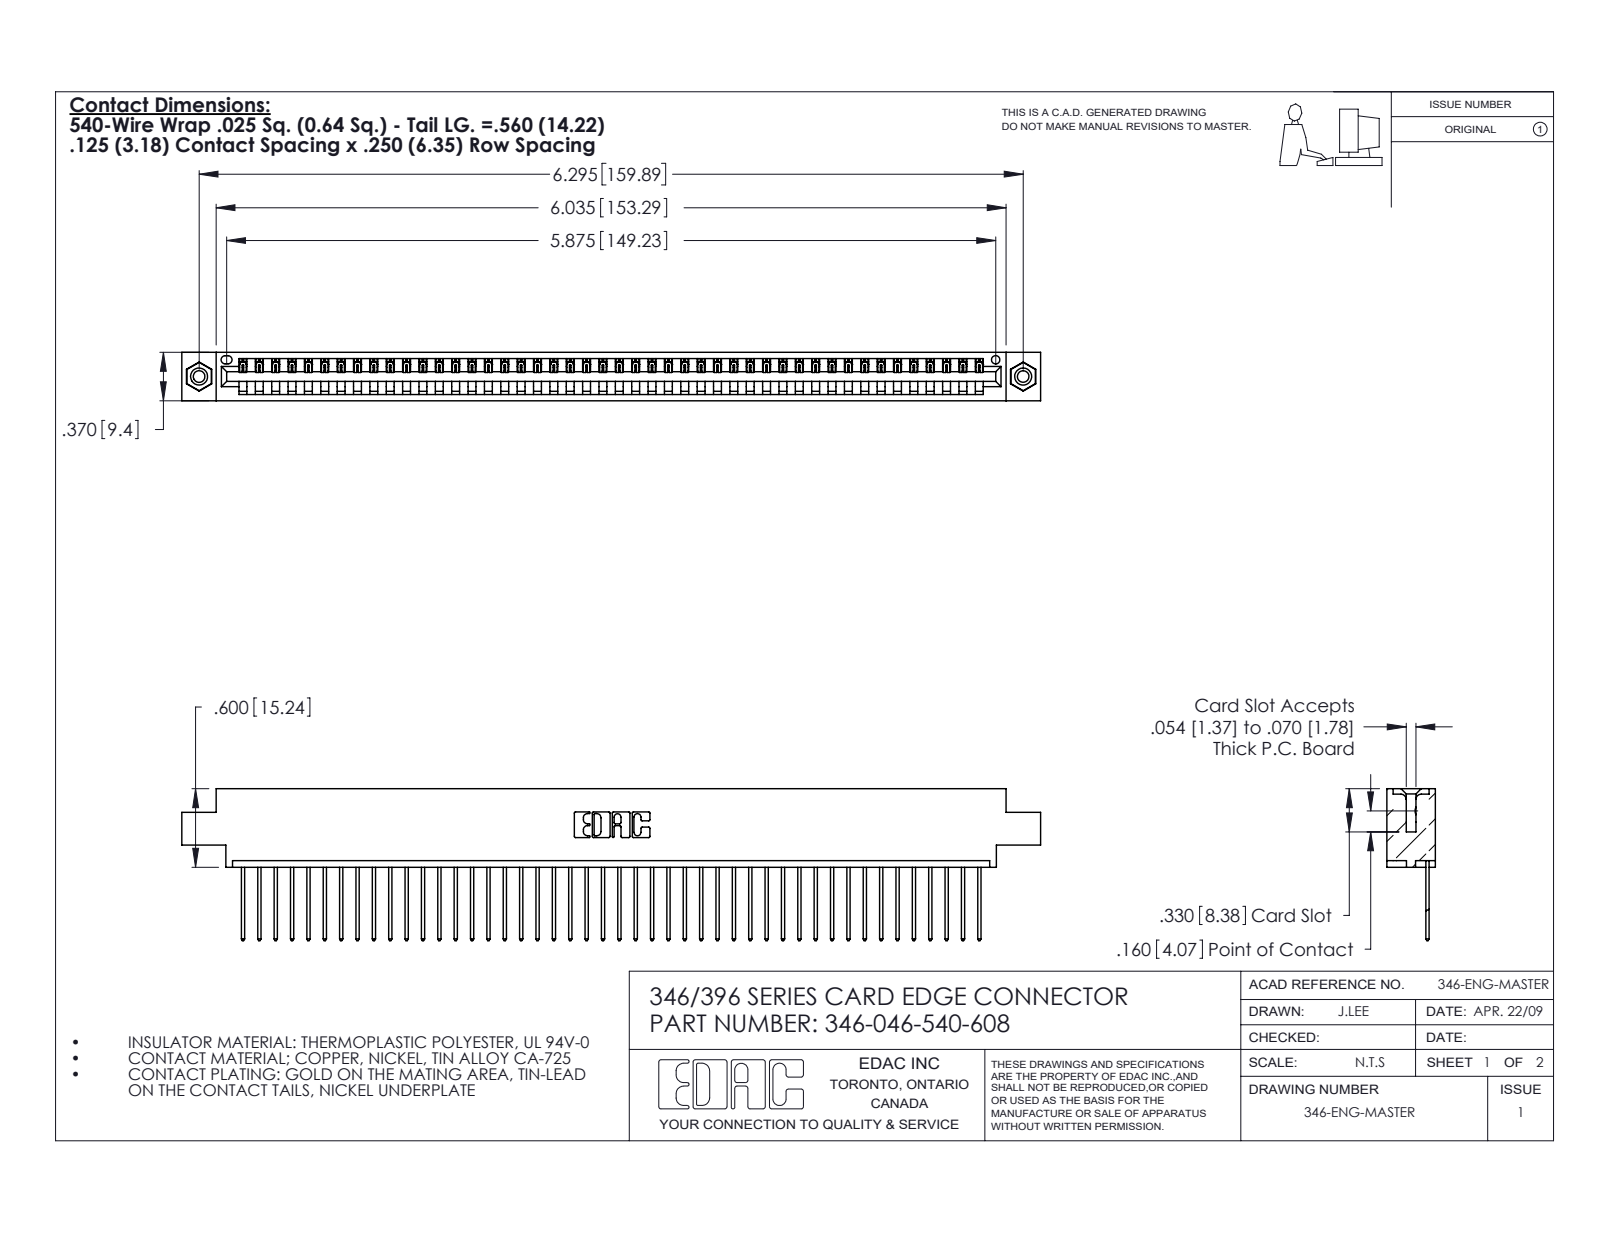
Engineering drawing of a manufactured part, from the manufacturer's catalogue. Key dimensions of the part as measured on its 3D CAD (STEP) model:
Part name (STEP PRODUCT): 345-292-001_345-293-140; 346-046-540-608; 346 Part_0.170 Offset - 0.156 Dia-TI; 345-250-001_345-250-003-102
STEP written by: SolidWorks 2020 (CONFIG_CONTROL_DESIGN)
Units: inches
Bodies: 49 solids, 2854 faces (1952 planar, 886 cylindrical, 16 other)
Overall size (bounding box): 6.56 × 1.16 × 0.37
Volume: 0.969 in³ · Surface area: 31.82 in²
Round holes (diameter × count): ⌀0.089 ×2, ⌀0.125 ×2, ⌀0.156 ×2, ⌀0.064 ×1
Round bosses / shafts (diameter × count): ⌀0.155 ×2
Partial cylindrical surfaces — rounded edges, fillets, slot ends (radius × count): R0.006 ×92, R0.01 ×92, R0.01 ×22, R0.007 ×6, R0.031 ×6, R0.026 ×3, R0.031 ×2, R0.04 ×2
Main face-to-face distances: 0.048, 0.322, 0.37, 0.25, 0.072, 0.298, 0.025, 0.222, 0.148, 0.1
Hole centre spacings: 0.246, 6.086, 6.295
